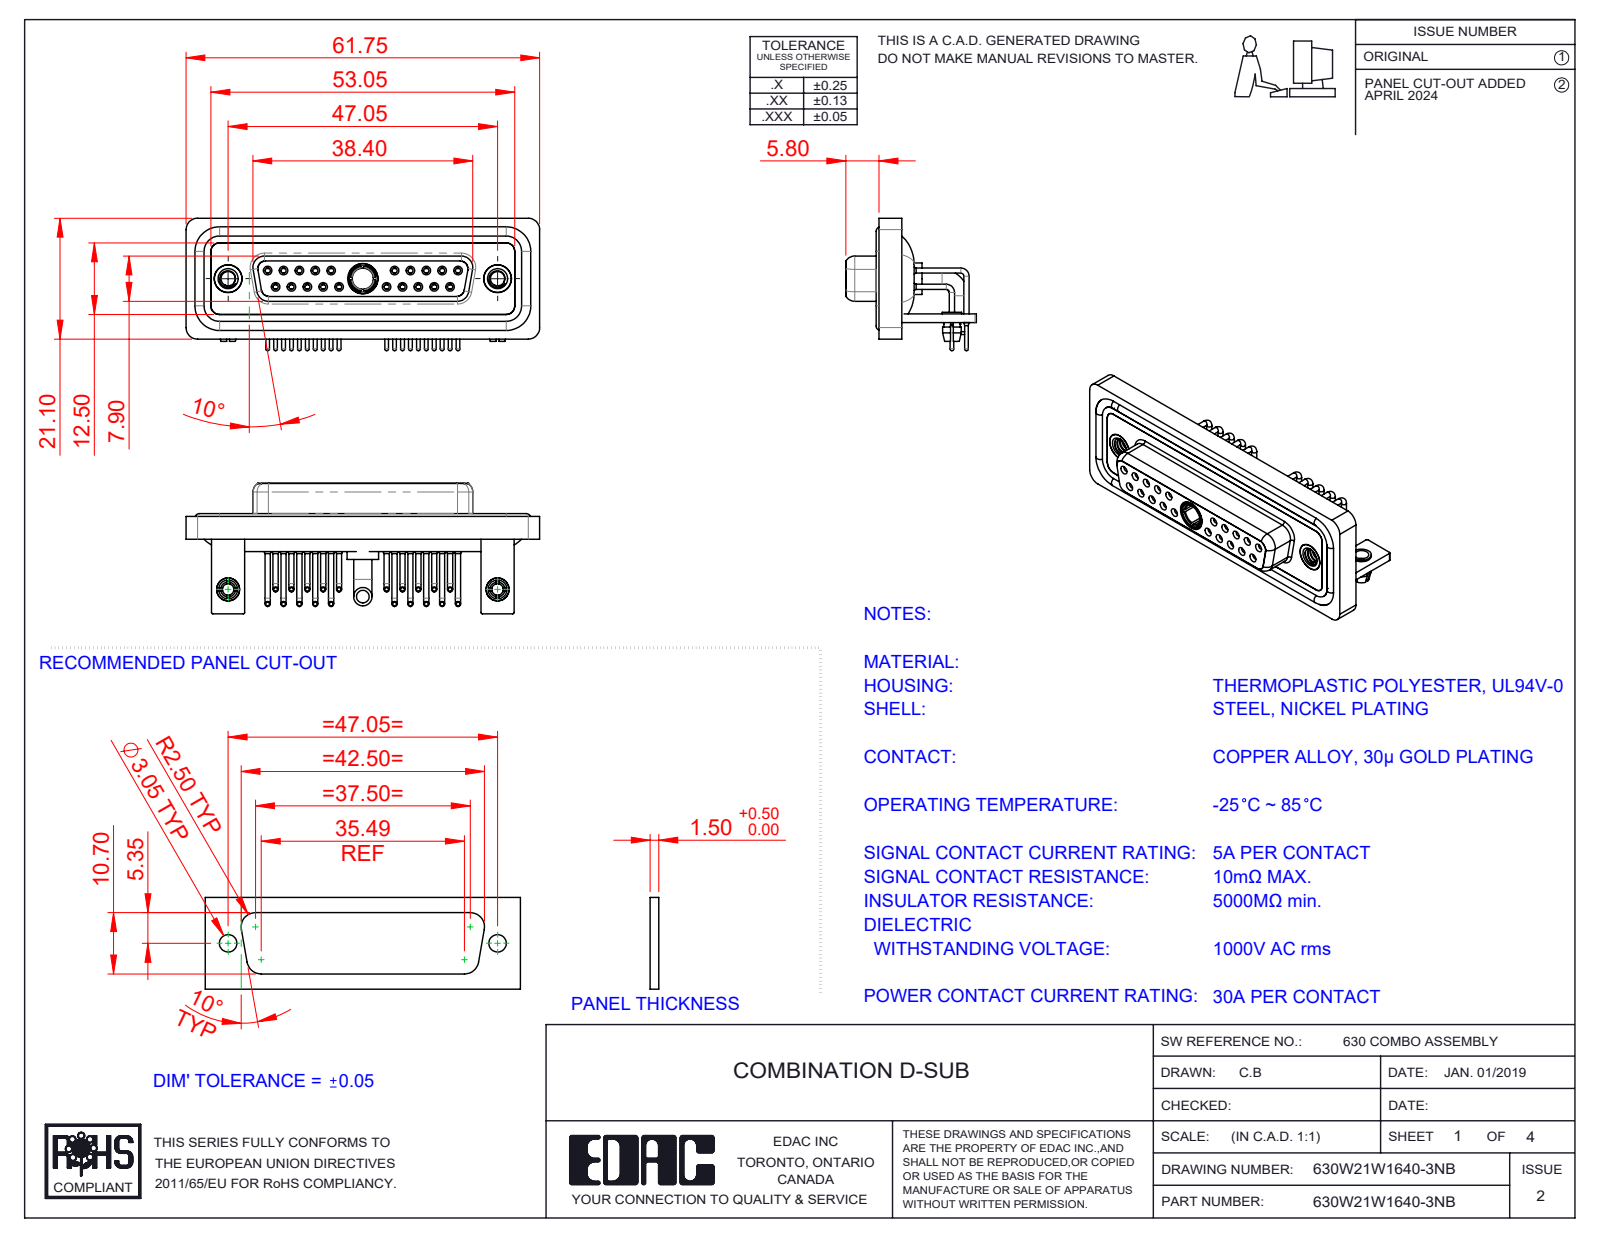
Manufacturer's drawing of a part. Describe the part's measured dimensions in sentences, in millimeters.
The part is named "630Combo Contact Row 1_50 Contacts; 630Combo Housing_21W1; 630Combo Shell Front_25 Contacts; 630Combo Waterproof Housing_25 Contacts (+7 more)". Its 3-D file was written by "SolidWorks 2023 (CONFIG_CONTROL_DESIGN)". It is 33 solids with 1658 faces: 502 planar, 727 cylindrical and 429 other. Overall it measures 61.75 by 23.12 by 22.8 millimeters. Its volume is 8 929 cubic millimeters and its surface area 15 747 square millimeters. Round holes: 22 of diameter 2, 20 of diameter 0.9, 20 of diameter 1.1, 20 of diameter 1.5, 10 of diameter 1.6, 10 of diameter 1.7, 4 of diameter 2.5, 3 of diameter 4.85, 2 of diameter 3.2, 2 of diameter 4, 2 of diameter 4.05, 2 of diameter 5. Round bosses or shafts: 20 of diameter 0.9, 20 of diameter 0.65, 14 of diameter 1.6, 2 of diameter 4.95, 2 of diameter 4.8, 2 of diameter 4, 2 of diameter 3.4, 2 of diameter 3.3. Partial cylindrical surfaces (rounded edges, fillets, slot ends): 19 of radius 2, 18 of radius 1.5, 16 of radius 0.25, 8 of radius 1.35, 8 of radius 1.6, 5 of radius 0.5, 4 of radius 0.6, 4 of radius 0.65. The main face-to-face distances are 0.4, 1.8, 2.9, 3.7, 1.5, 4.1, 1.1, 1.4, 1.6, 2.5. The hole center spacings are 3.16, 2.77, 5.54, 8.31, 5.04, 19.39, 20.97, 22.16.
